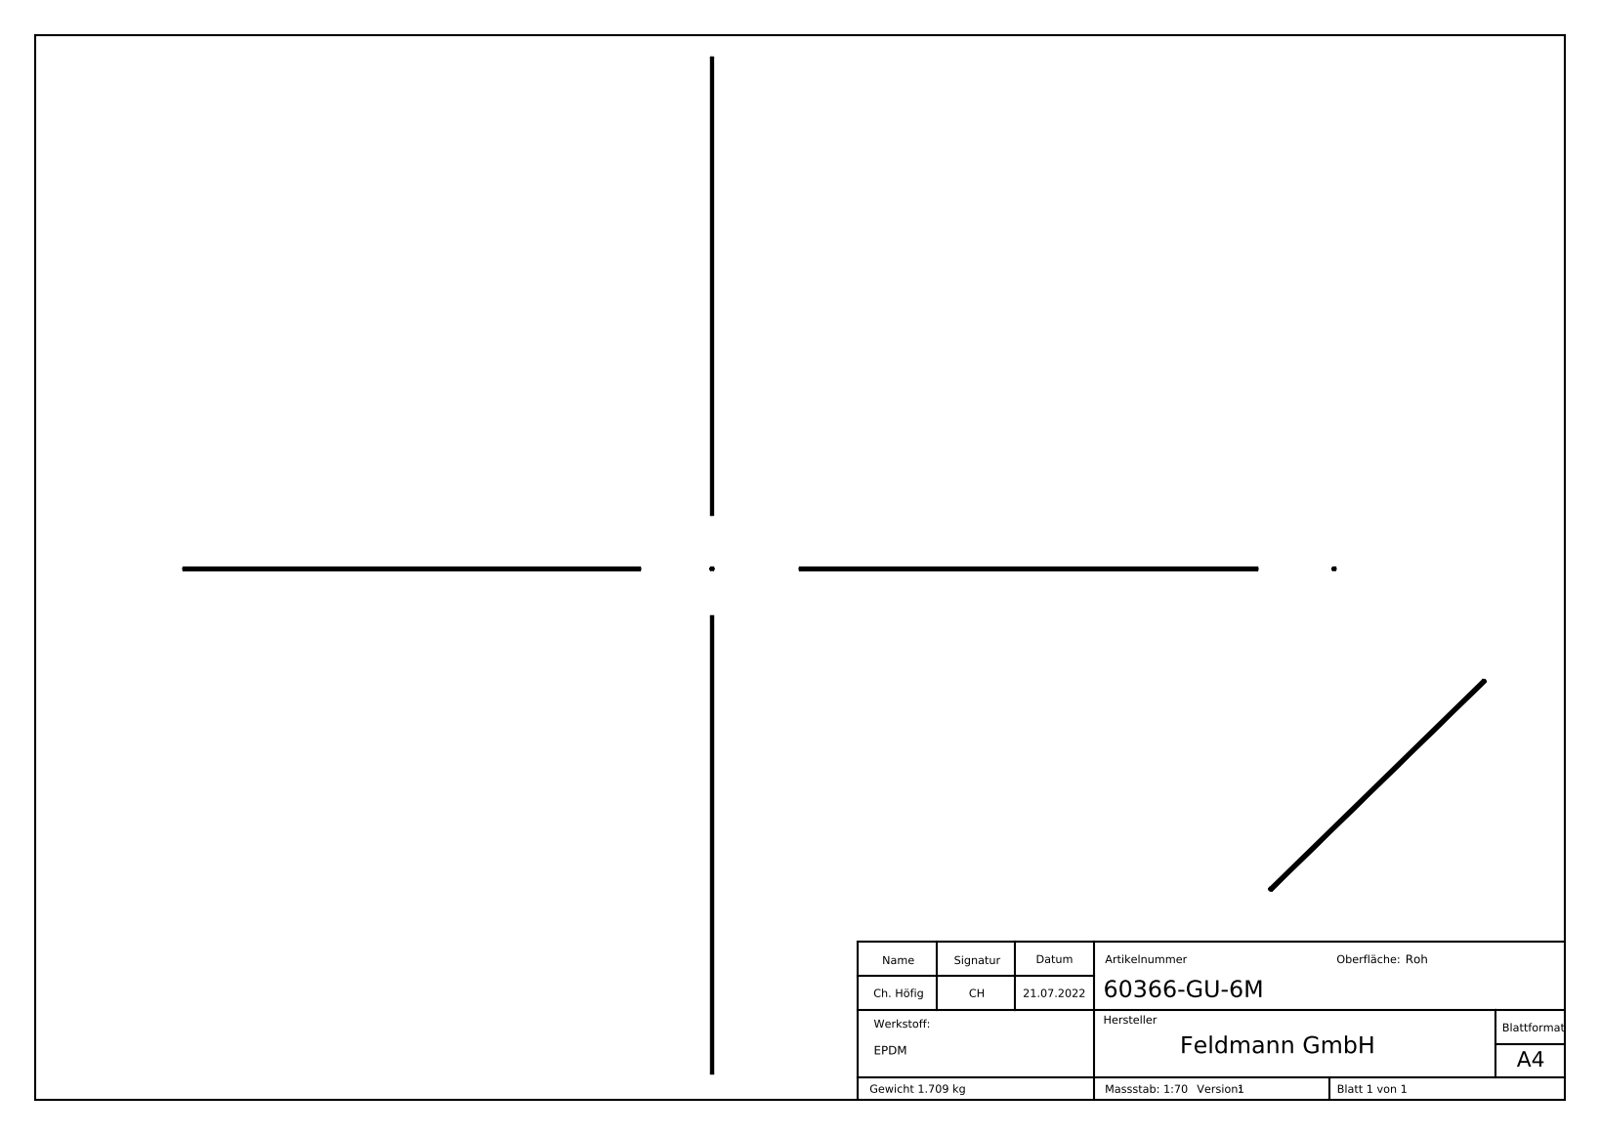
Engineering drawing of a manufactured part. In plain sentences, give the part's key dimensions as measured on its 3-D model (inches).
The part is named "60366-GU-6M". Its 3-D file was written by "SolidWorks 2018 (CONFIG_CONTROL_DESIGN)". It is 1 solid with 377 faces: 224 planar, 10 cylindrical and 143 other. Overall it measures 236.22 by 1.371 by 1.28 inches. Its volume is 88.3 cubic inches and its surface area 2 616 square inches. Partial cylindrical surfaces (rounded edges, fillets, slot ends): 4 of radius 0.02, 2 of radius 0.047, 2 of radius 0.157, 2 of radius 0.394. The main face-to-face distances are 0.059, 1.004, 0.098, 0.199, 0.259, 0.459, 0.945, 1.063, 0.068, 0.2.
